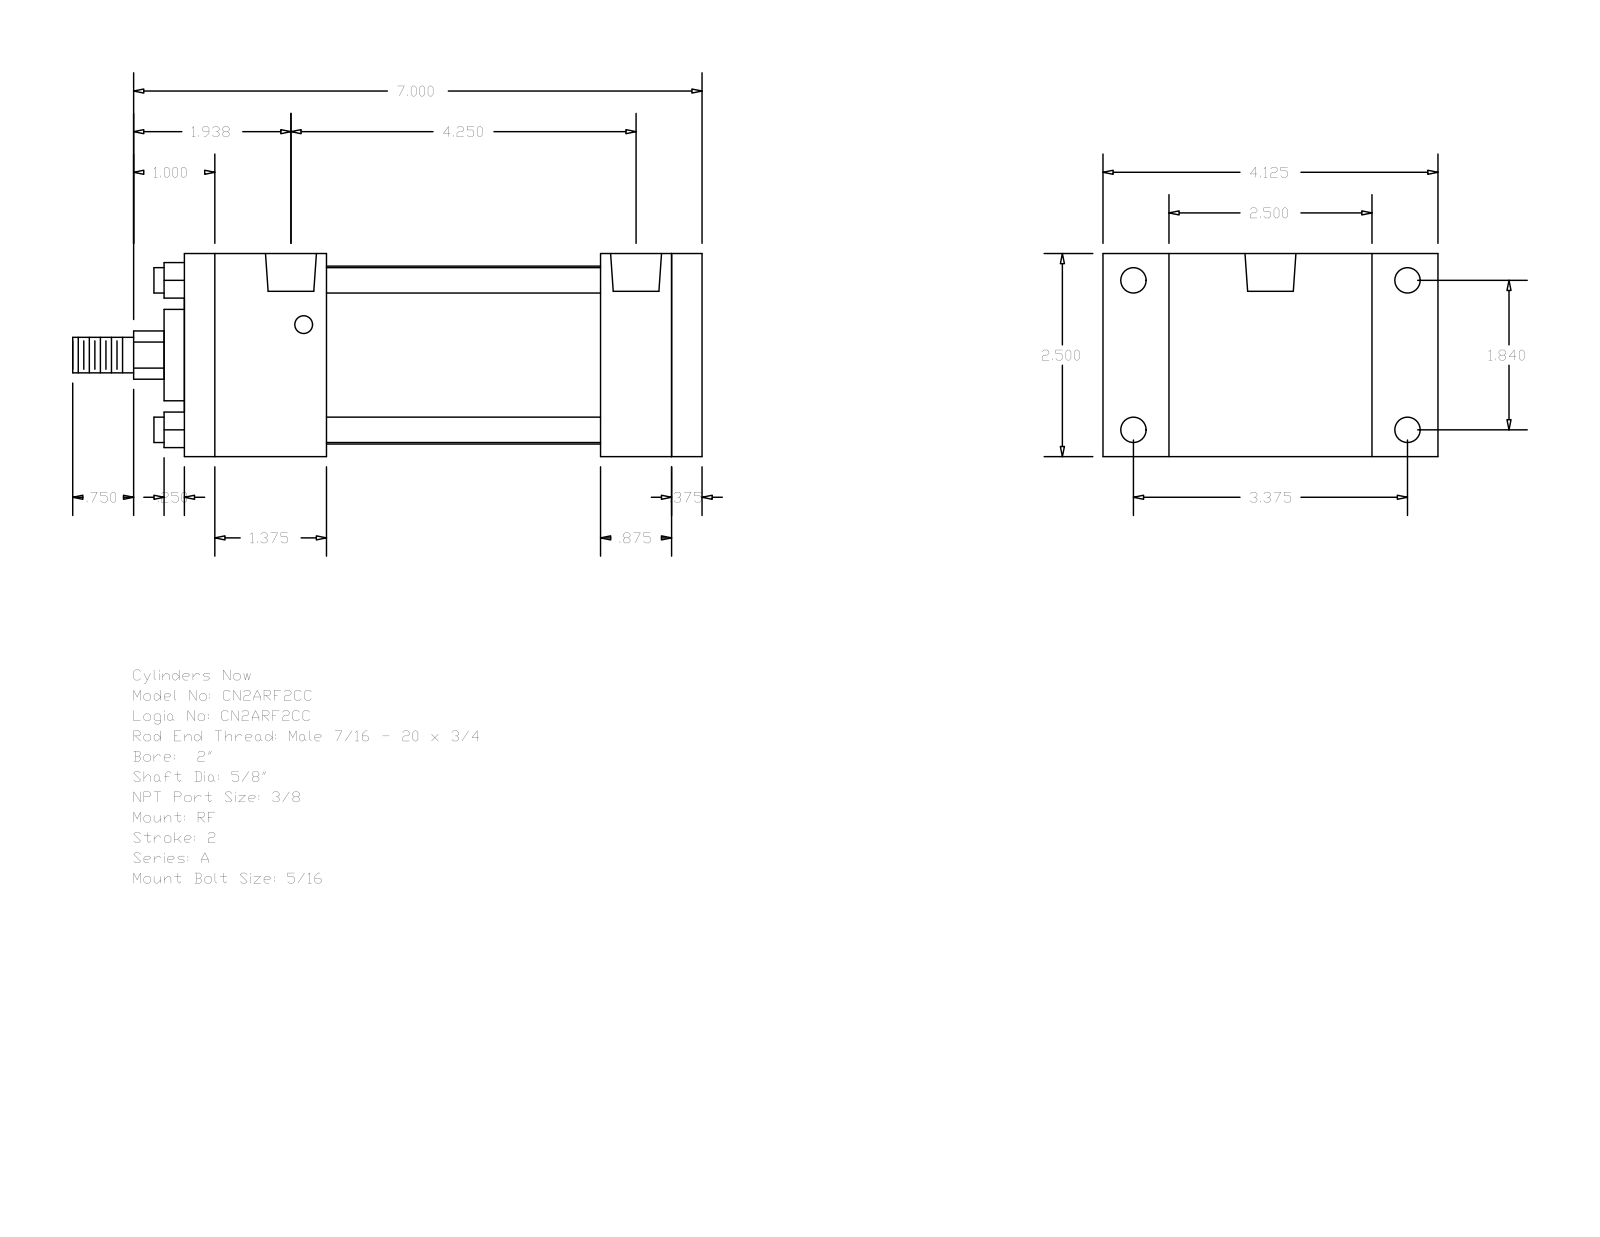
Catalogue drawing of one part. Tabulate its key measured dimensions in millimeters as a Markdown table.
| quantity | value |
| --- | --- |
| part name | A_RF__0200_0.625 |
| STEP written by | GSSL Pune (CONFIG_CONTROL_DESIGN) |
| units | millimeters |
| bodies | 0 solids, 92 faces (64 planar, 28 cylindrical, 0 other) |
| overall size | 196.85 × 104.78 × 63.5 |
| round holes (diameter × count) | 5.56 × 4, 7.94 × 4, 15.93 × 2 |
| round bosses / shafts (diameter × count) | 7.94 × 4, 55.63 × 1, 28.57 × 1, 15.88 × 1, 11.11 × 1 |
| partial cylindrical surfaces (radius × count) | 7.54 × 1 |
| main face-to-face distances | 63.5, 161.92, 152.4, 9.52, 44.45, 107.95, 117.47, 130.17, 85.72, 22.23 |
| hole center spacings | 46.74, 85.72, 97.63, 100, 3.97, 3.98, 103.97, 103.98 |
